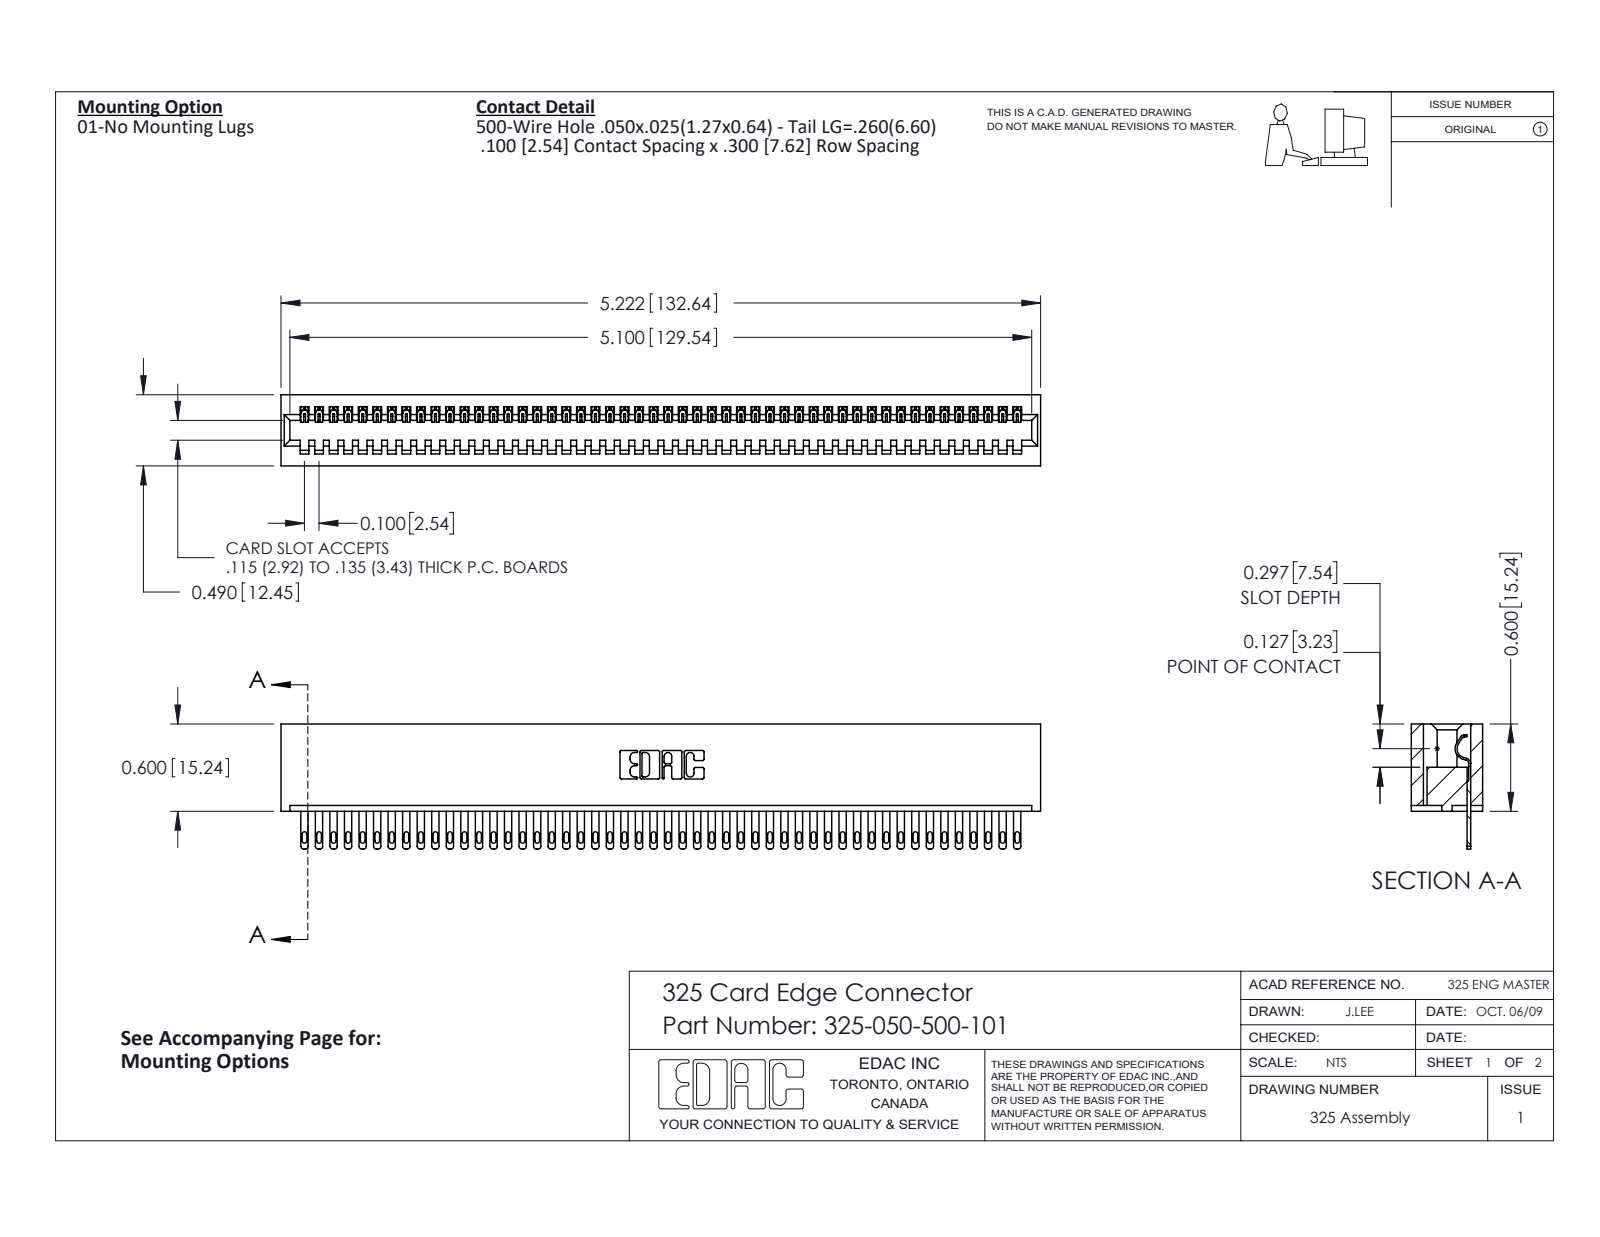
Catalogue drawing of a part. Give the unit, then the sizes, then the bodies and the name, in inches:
Units: inches
Overall size (bounding box): 5.222 × 0.86 × 0.49
Partial cylindrical surfaces — rounded edges, fillets, slot ends (radius × count): R0.006 ×100, R0.016 ×100, R0.02 ×100, R0.01 ×22, R0.007 ×6, R0.031 ×6, R0.026 ×3, R0.014 ×1
Main face-to-face distances: 0.083, 0.407, 0.49, 0.3, 0.107, 0.383, 0.025, 0.325, 0.56, 0.263
Volume: 1.068 in³ · Surface area: 30.79 in²
Bodies: 51 solids, 2806 faces (1866 planar, 940 cylindrical, 0 other)
Part name (STEP PRODUCT): 325-292-001_325-293-100; 325-050-500-101; 325 Part_Lugless
STEP written by: SolidWorks 2016 (CONFIG_CONTROL_DESIGN)
